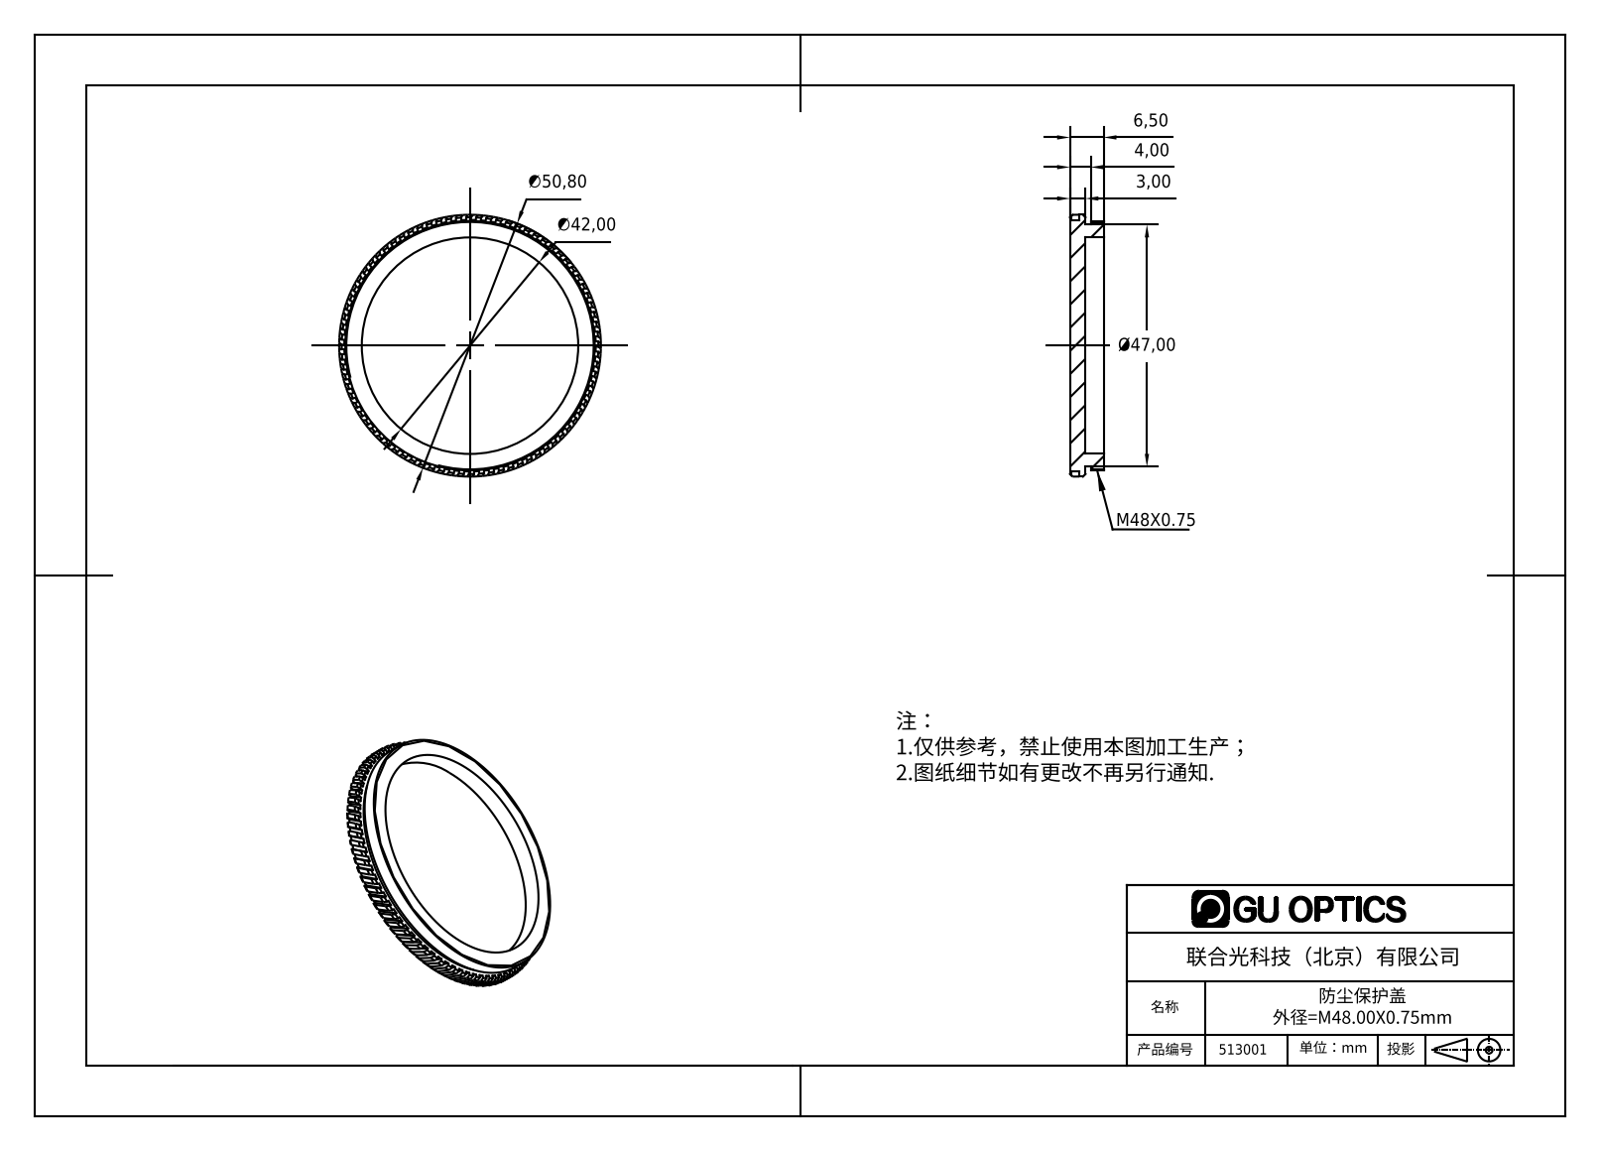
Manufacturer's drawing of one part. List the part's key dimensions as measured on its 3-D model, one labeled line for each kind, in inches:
Part name (STEP PRODUCT): 513001
STEP written by: SolidWorks 2016 (AUTOMOTIVE_DESIGN)
Units: inches
Bodies: 1 solid, 574 faces (165 planar, 247 cylindrical, 162 other)
Overall size (bounding box): 2 × 2 × 0.256
Volume: 0.447 in³ · Surface area: 9.382 in²
Round holes (diameter × count): ⌀1.654 ×1
Round bosses / shafts (diameter × count): ⌀2 ×1, ⌀1.921 ×1, ⌀1.906 ×1, ⌀1.85 ×1
Main face-to-face distances: 0.118, 0.138, 0.256, 0.031, 0.098, 0.039, 0.157, 0.032
